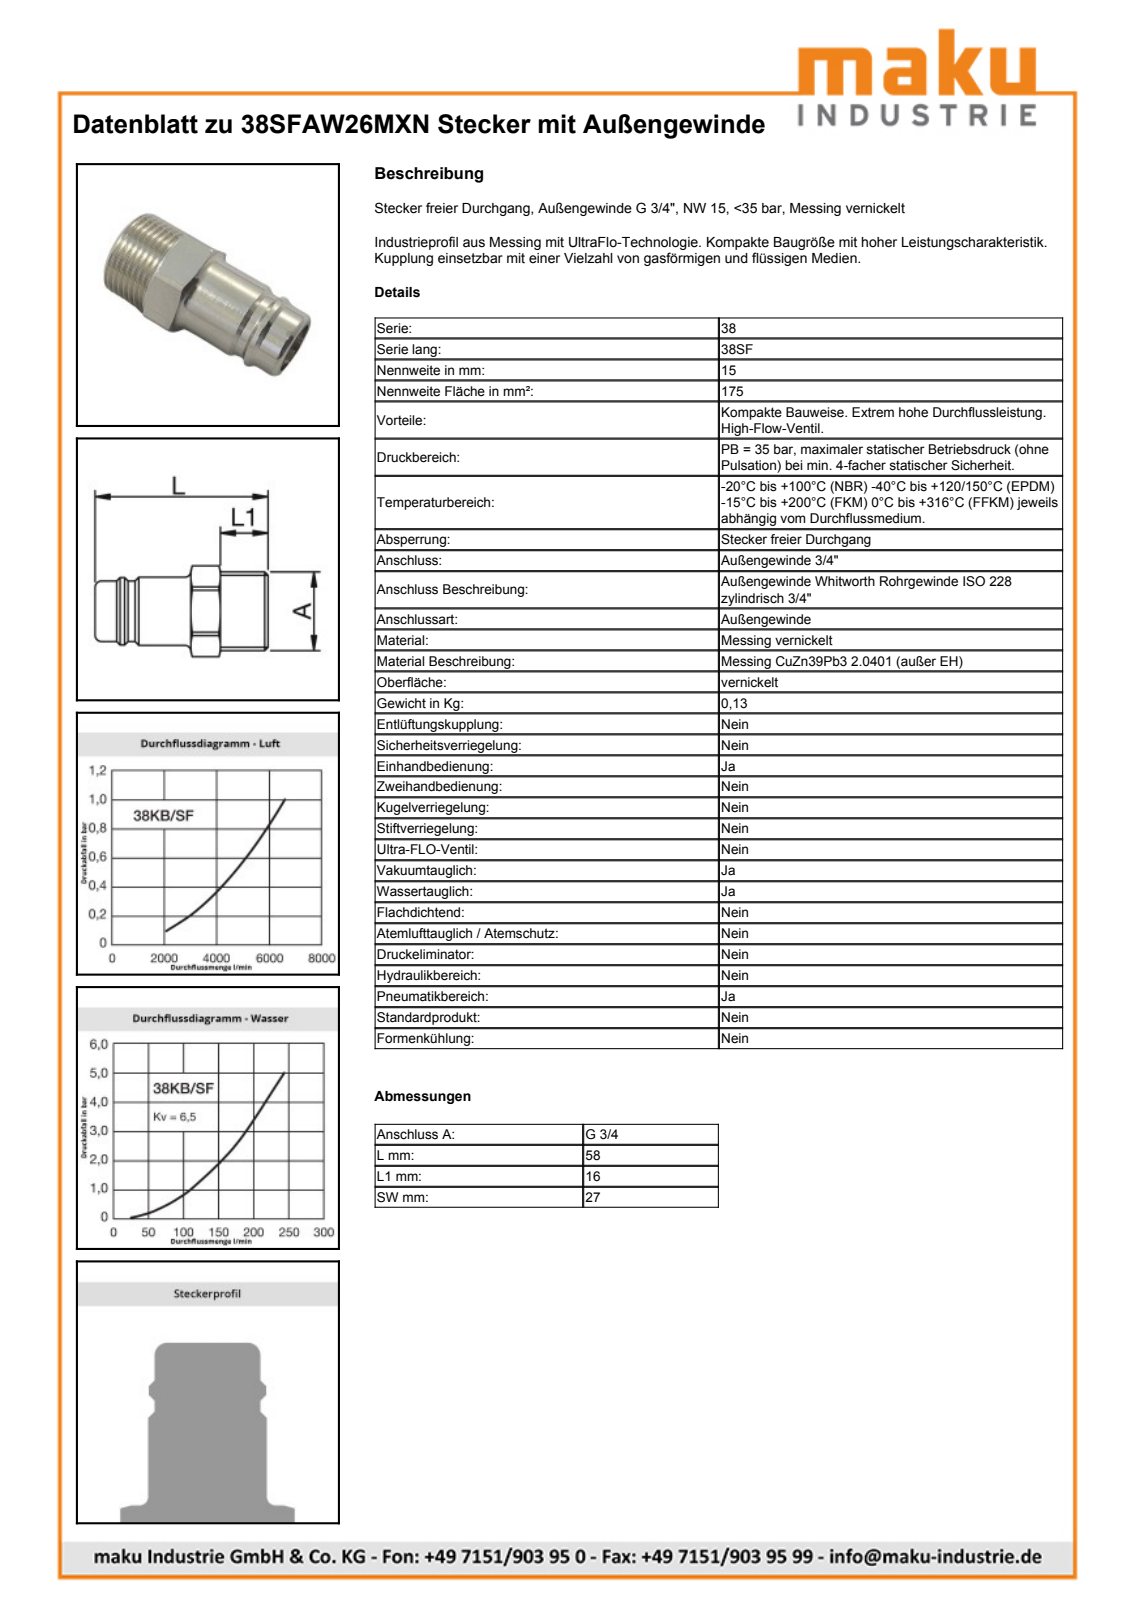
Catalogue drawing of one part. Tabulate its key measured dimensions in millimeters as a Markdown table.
| quantity | value |
| --- | --- |
| part name | D108772; D108764; D105913 |
| STEP written by | Autodesk Inventor 2013 (AUTOMOTIVE_DESIGN) |
| units | millimeters |
| bodies | 2 solids, 46 faces (13 planar, 15 cylindrical, 18 other) |
| overall size | 54 × 27.05 × 25.5 |
| volume | 13 123 mm³ |
| surface area | 7 347 mm² |
| round holes (diameter × count) | 14 × 1, 21.2 × 1 |
| round bosses / shafts (diameter × count) | 25.5 × 1, 22.85 × 1, 22.6 × 1, 20.96 × 1, 20.3 × 1 |
| partial cylindrical surfaces (radius × count) | 13.53 × 1 |
| main face-to-face distances | 24, 2, 12, 10, 42, 44, 54, 1.75, 22.25, 20.5 |
